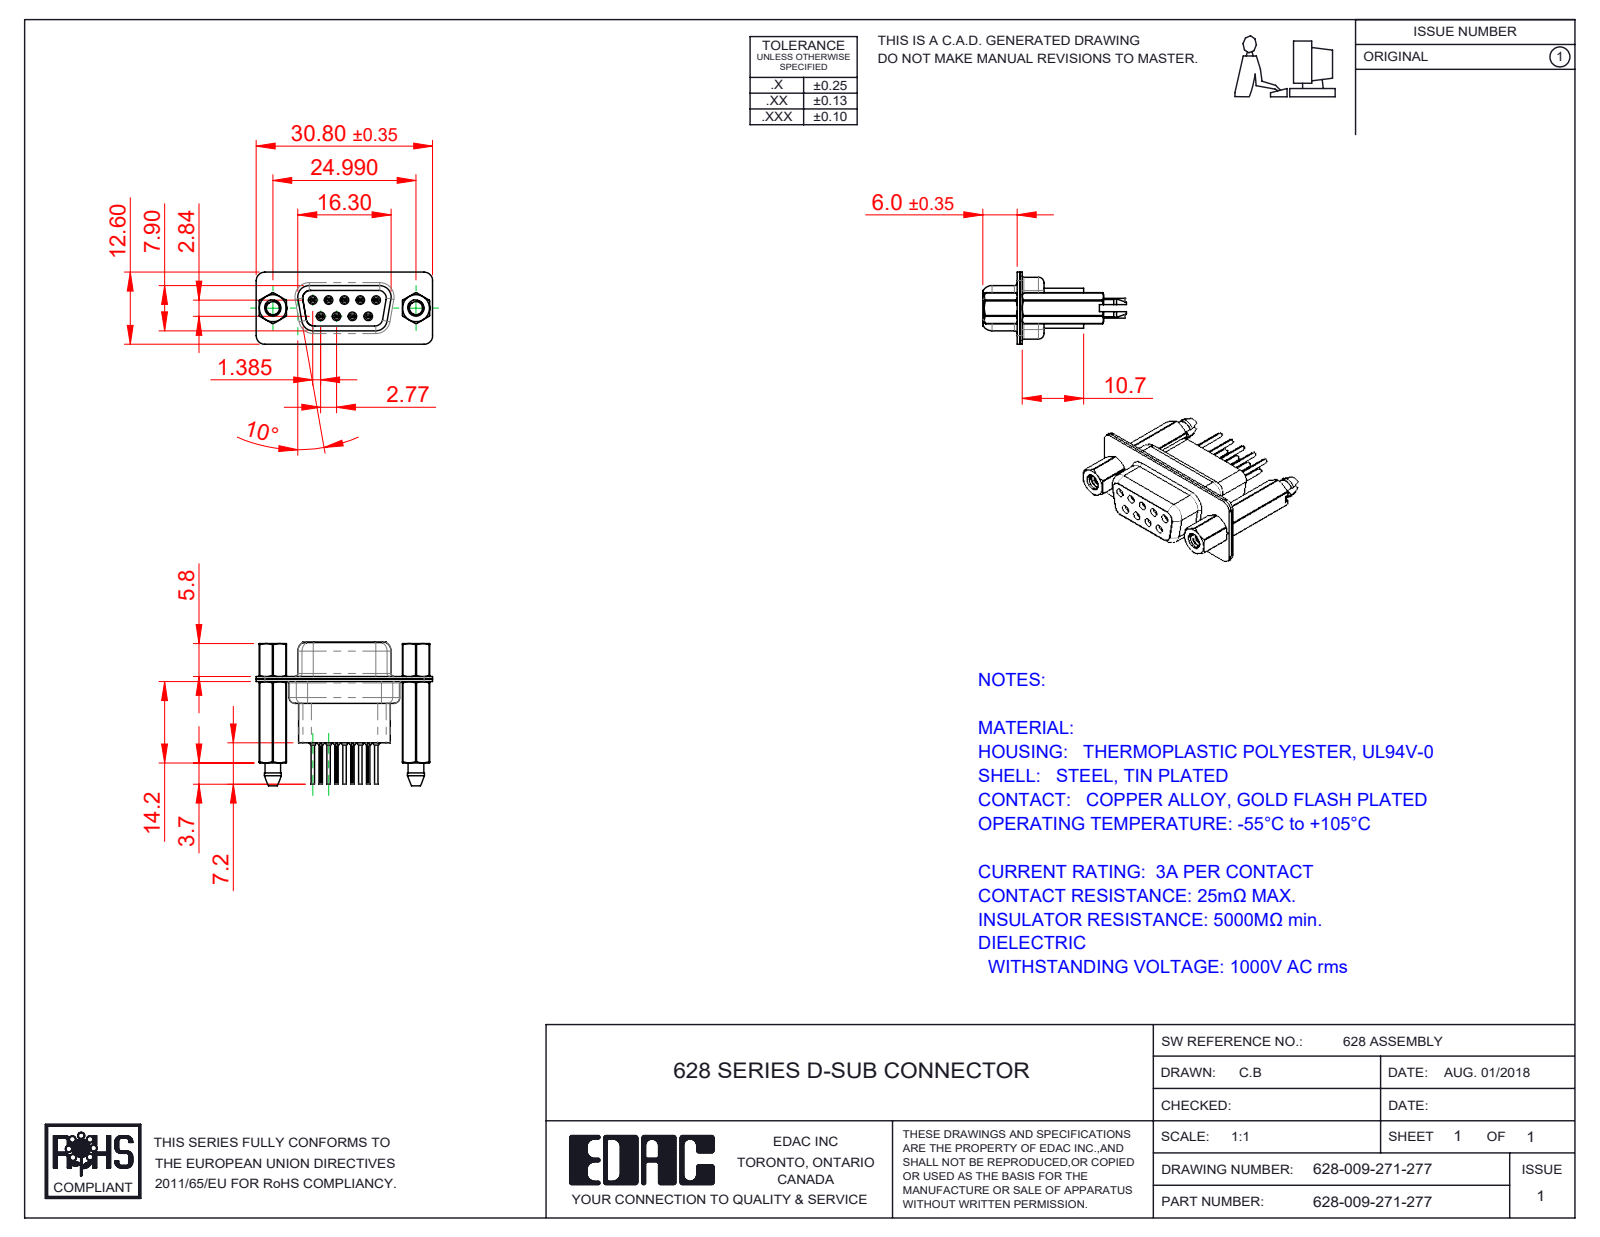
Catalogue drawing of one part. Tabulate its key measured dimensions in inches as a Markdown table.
| quantity | value |
| --- | --- |
| part name | 628 4-40 Threaded Boardlock_HP71; 628-009-271-277; 628 Housing_09 HP; 628 4-40 Hex Standoff (+4 more) |
| STEP written by | SolidWorks 2020 (CONFIG_CONTROL_DESIGN) |
| units | inches |
| bodies | 16 solids, 1586 faces (400 planar, 538 cylindrical, 648 other) |
| overall size | 1.213 × 0.988 × 0.496 |
| volume | 0.172 in³ |
| surface area | 10.18 in² |
| round holes (diameter × count) | 0.008 × 9, 0.031 × 9, 0.035 × 9, 0.043 × 9, 0.063 × 9, 0.067 × 5, 0.089 × 2, 0.09 × 2, 0.157 × 2, 0.159 × 2, 0.191 × 2 |
| round bosses / shafts (diameter × count) | 0.079 × 9, 0.059 × 9, 0.047 × 9, 0.024 × 9, 0.195 × 2, 0.189 × 2, 0.11 × 2 |
| partial cylindrical surfaces (radius × count) | 0.059 × 19, 0.004 × 18, 0.079 × 12, 0.011 × 9, 0.053 × 6, 0.063 × 6, 0.01 × 4, 0.02 × 4 |
| main face-to-face distances | 0.018, 0.016, 0.035, 0.187, 0.335, 0.26, 0.075, 0.055, 0.276, 0.02 |
| hole center spacings | 0.124, 0.109, 0.218, 0.198, 0.198, 0.327, 0.294, 0.295 |
